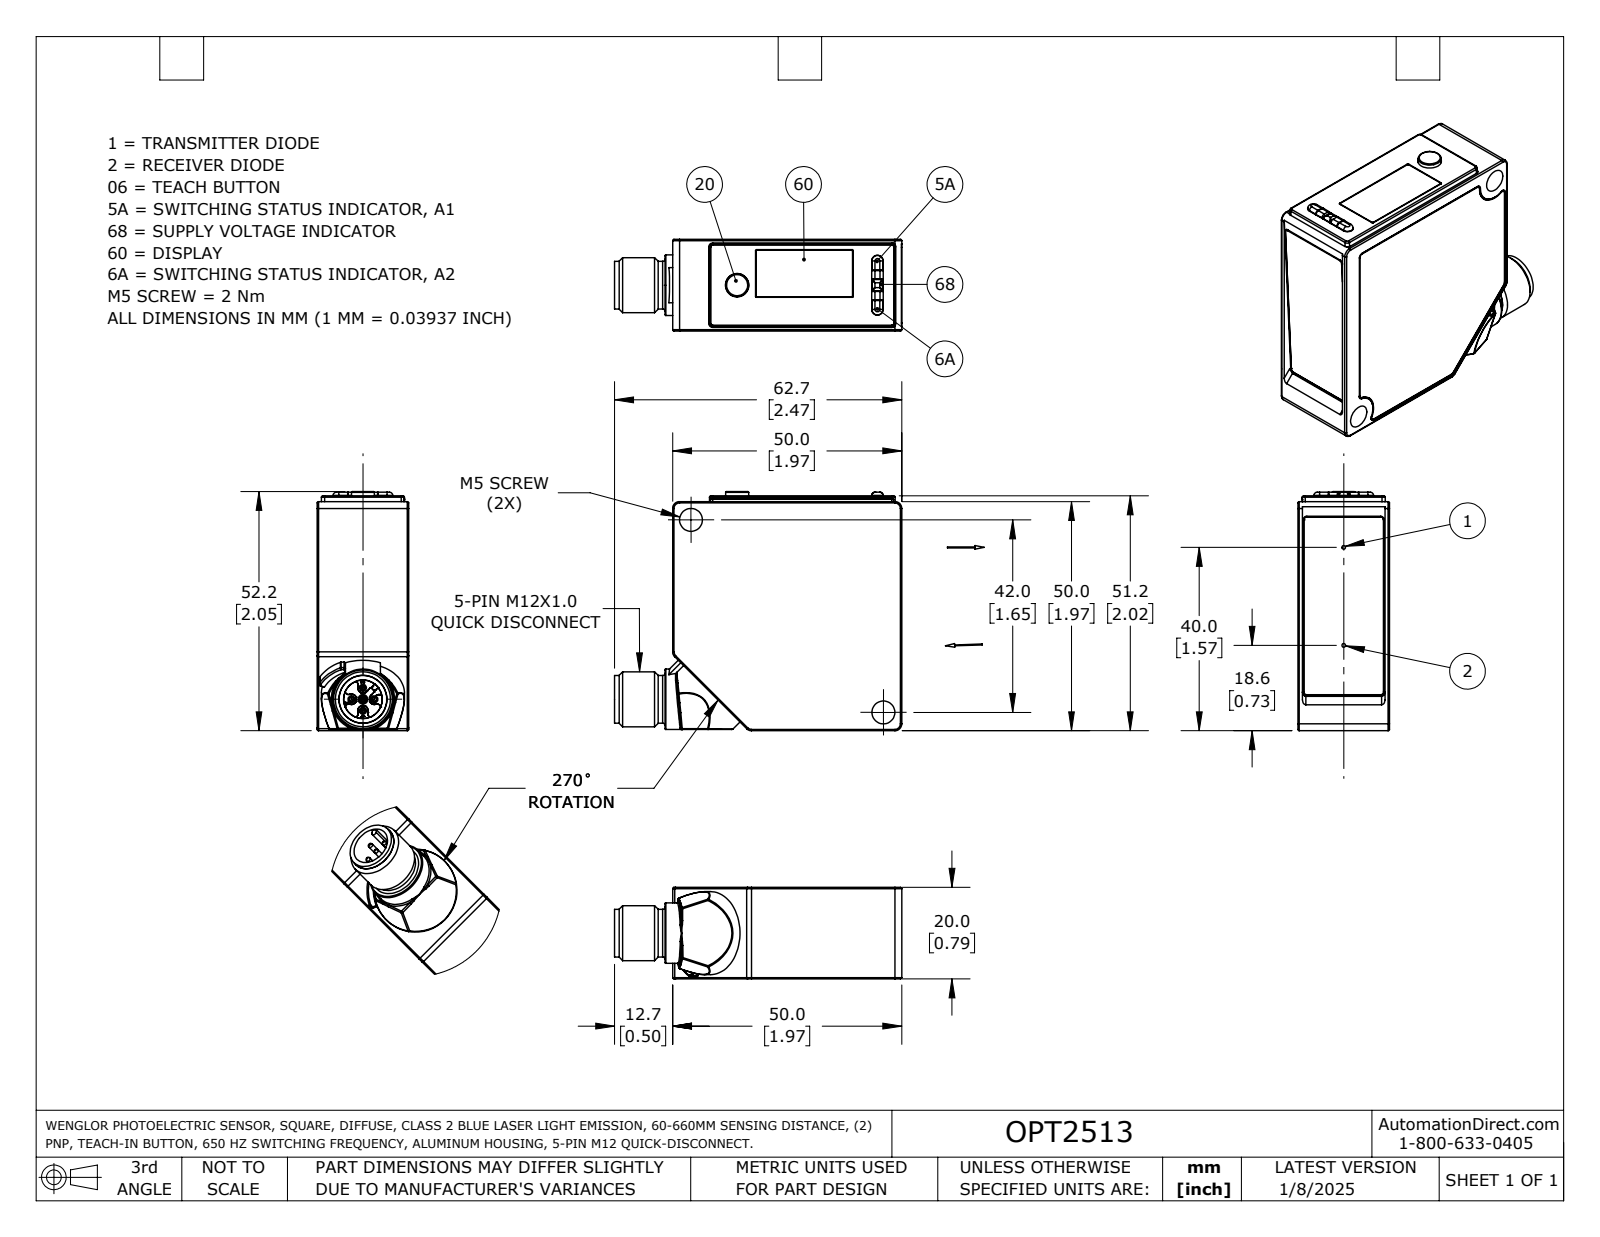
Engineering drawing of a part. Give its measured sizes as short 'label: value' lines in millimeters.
name: OPT2502_OPT2505_OPT2508_OPT2511_OPT2513_OPT2514
written by: SolidWorks 2024 (AUTOMOTIVE_DESIGN)
unit: mm
bodies: 2 solids, 433 faces (182 planar, 133 cylindrical, 118 other)
size: 80.7 × 52.2 × 20
holes: 5× ⌀1.5, 2× ⌀4.1, 1× ⌀5.1
bosses: 5× ⌀1, 2× ⌀0.2, 1× ⌀18.1, 1× ⌀13.2, 1× ⌀12, 1× ⌀10.4, 1× ⌀5, 1× ⌀2.1
rounds: 35× R0.3, 11× R0.7, 8× R0.2, 7× R0.8, 6× R0.7, 6× R0.7, 6× R0.8, 5× R1.5
face distances: 19.9, 51.2, 20, 50, 1.2, 0.9, 49.7, 51, 19, 1
hole spacings: 2.5, 3.5, 5, 59.4
